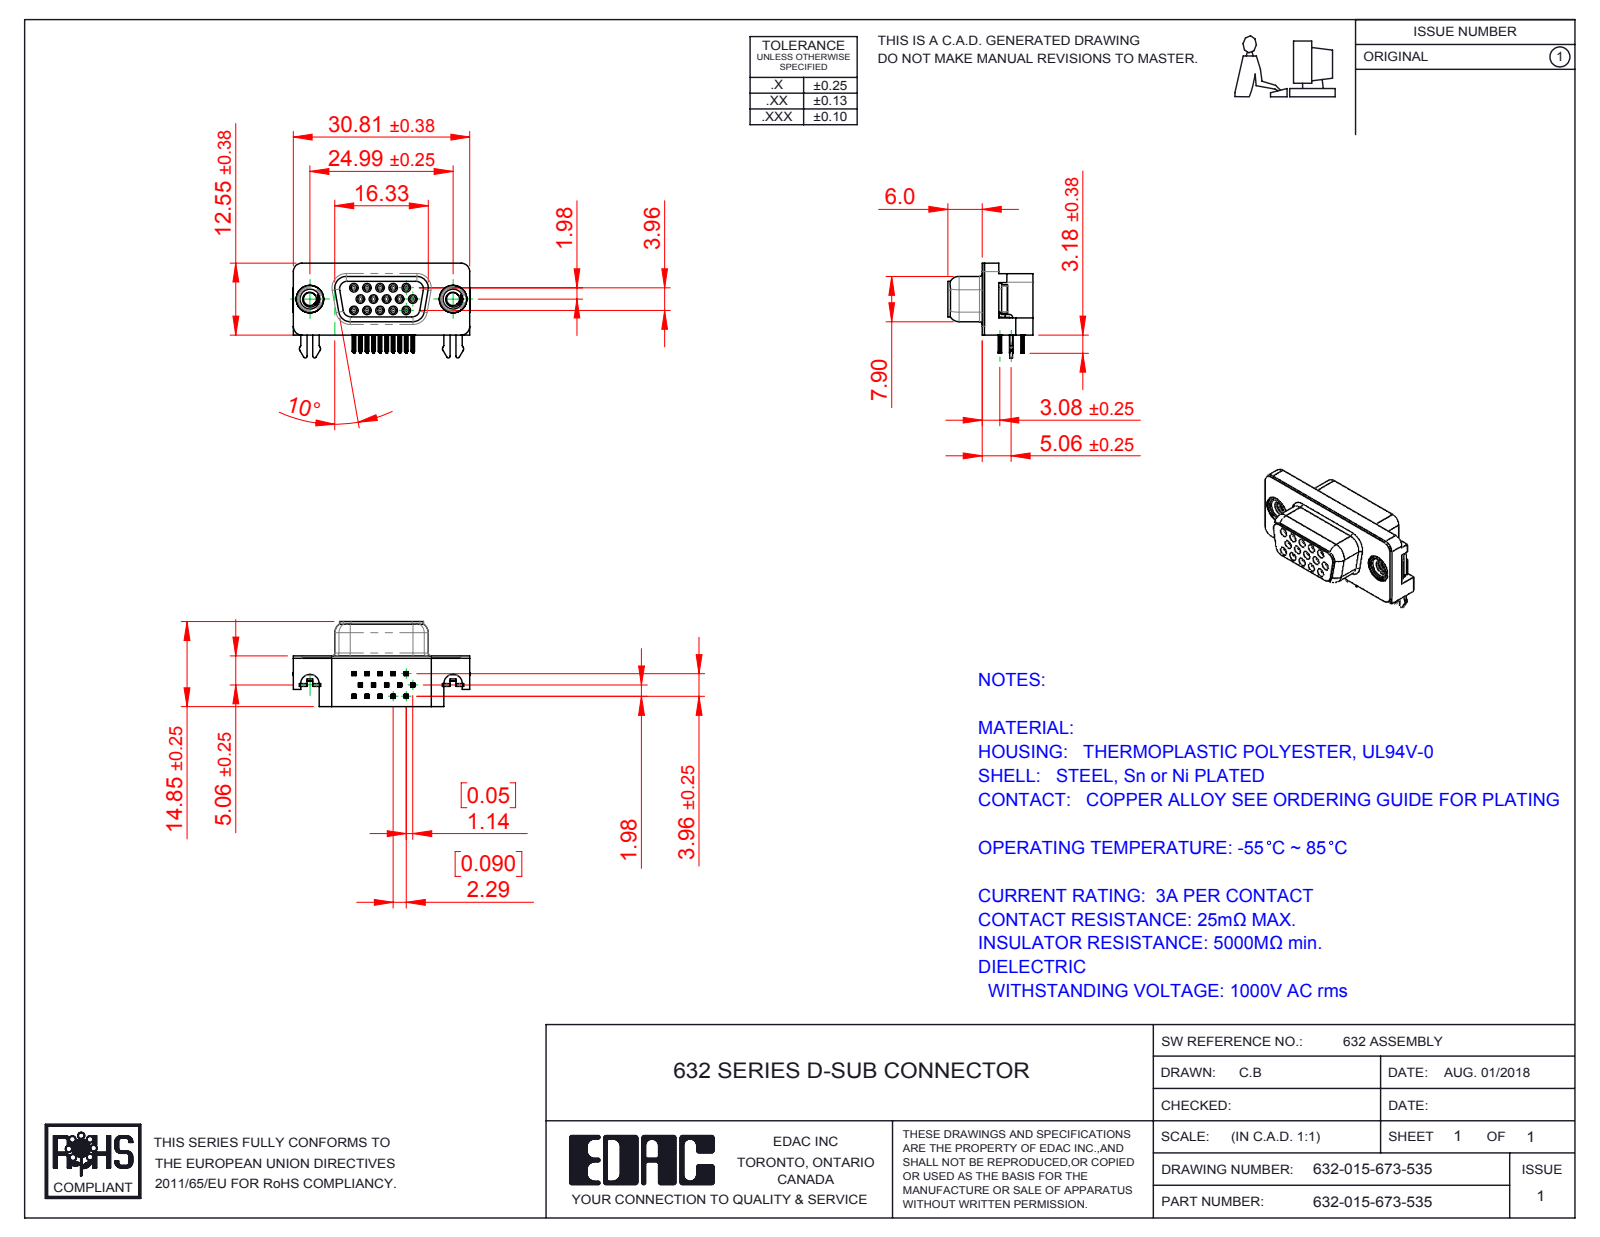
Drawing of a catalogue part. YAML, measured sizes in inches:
part_name: "632 Shell_9 Socket; 632 Housing_15 Socket; 632 M3 Threaded Rivet; 632 Contact Bottom (+6 more)"
step_written_by: "SolidWorks 2016 (CONFIG_CONTROL_DESIGN)"
units: inches
bodies: {solids: 23, faces: 2426, planar: 1006, cylindrical: 654, other: 766}
overall_size: [1.216, 0.652, 0.585]
volume: 0.183
surface_area: 8.275
round_holes:
  - {diameter: 0.031, count: 15}
  - {diameter: 0.035, count: 15}
  - {diameter: 0.089, count: 2}
  - {diameter: 0.098, count: 2}
  - {diameter: 0.157, count: 2}
  - {diameter: 0.189, count: 2}
  - {diameter: 0.197, count: 2}
round_bosses_or_shafts:
  - {diameter: 0.047, count: 15}
  - {diameter: 0.193, count: 2}
  - {diameter: 0.187, count: 2}
  - {diameter: 0.154, count: 2}
partial_cylinders:
  - {radius: 0.004, count: 120}
  - {radius: 0.006, count: 60}
  - {radius: 0.014, count: 30}
  - {radius: 0.013, count: 15}
  - {radius: 0.039, count: 11}
  - {radius: 0.011, count: 10}
  - {radius: 0.02, count: 10}
  - {radius: 0.01, count: 8}
face_to_face_distances: [0.016, 0.333, 0.348, 0.078, 0.114, 0.234, 0.098, 0.252, 0.264, 0.278]
hole_center_spacings: [0.09, 0.09, 0.156, 0.18, 0.238, 0.156, 0.18, 0.27]
